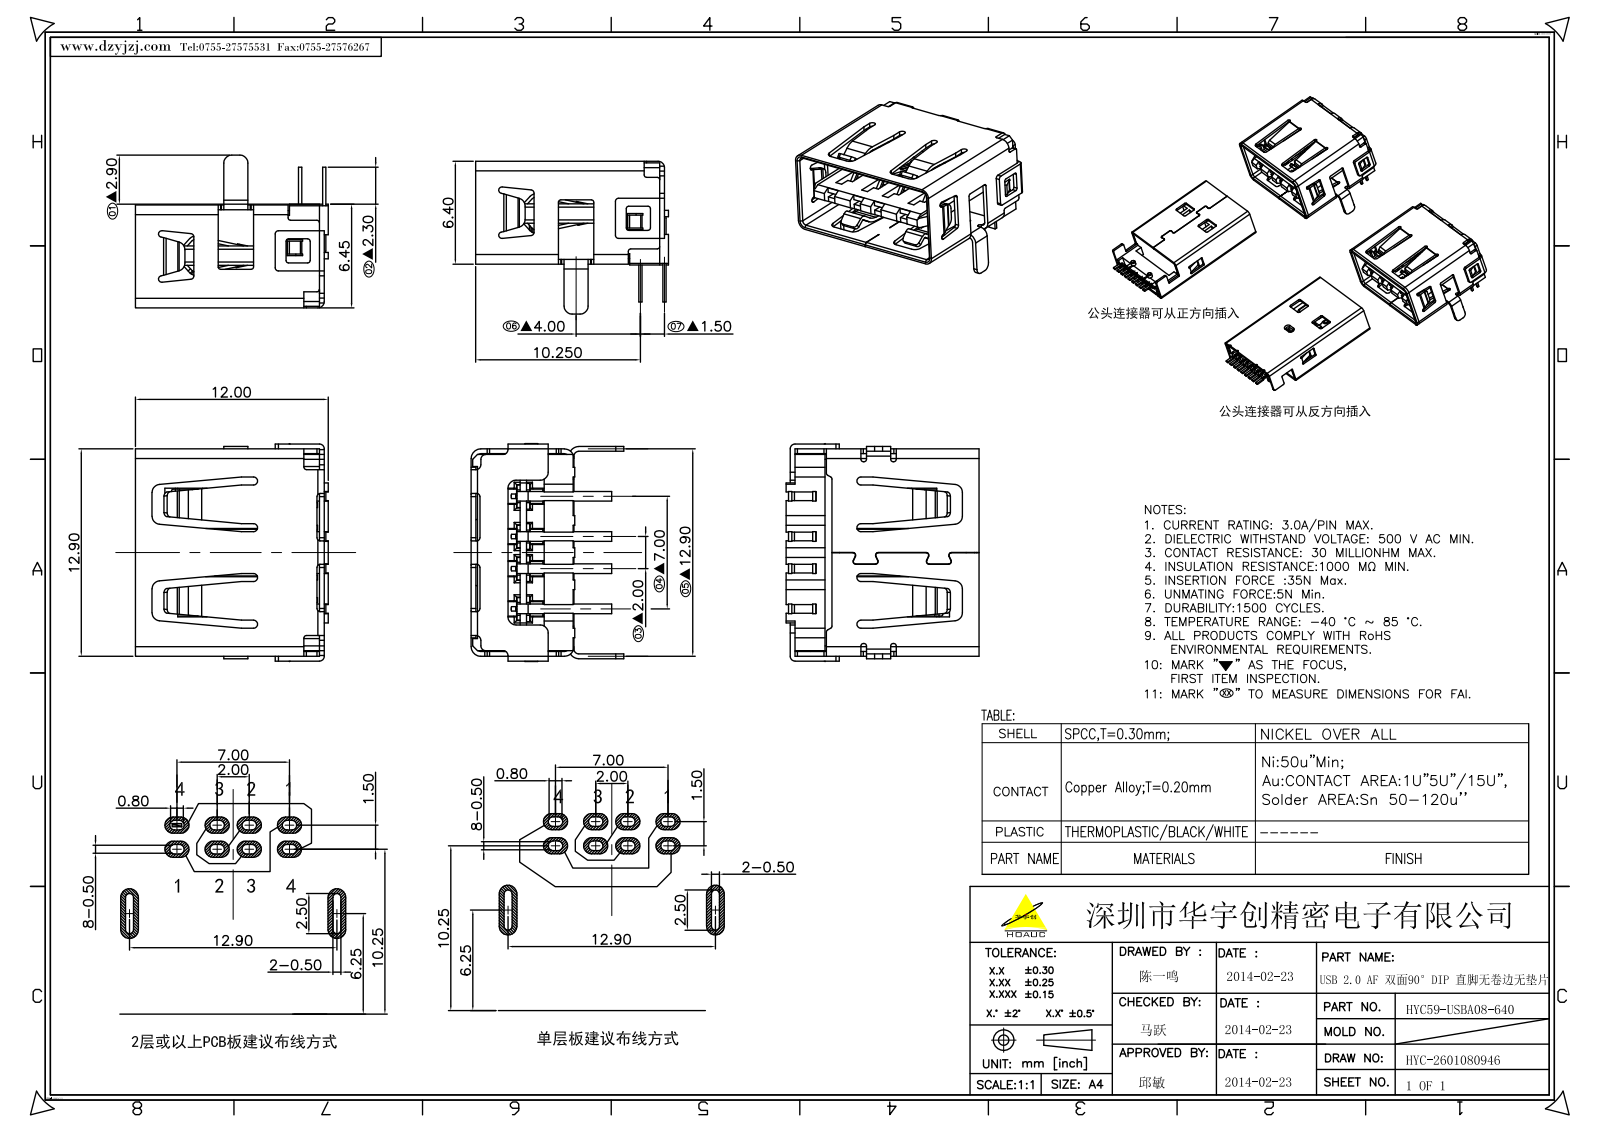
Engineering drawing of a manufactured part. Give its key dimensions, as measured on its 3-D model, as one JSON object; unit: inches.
{"part_name": "PRODUCT_2258", "step_written_by": "CREO PARAMETRIC BY PTC INC, 2022073 (AUTOMOTIVE_DESIGN)", "units": "inches", "bodies": {"solids": 1, "faces": 746, "planar": 507, "cylindrical": 215, "other": 24}, "overall_size": [0.533, 0.472, 0.374], "volume_in3": 0.027, "surface_area_in2": 2.128, "partial_cylinders_radius": [[0.006, 32], [0.008, 24], [0.012, 20], [0.004, 19], [0.02, 17], [0.01, 12], [0.024, 10], [0.007, 8]], "face_to_face_distances": [0.24, 0.136, 0.089, 0.14, 0.1, 0.228, 0.252, 0.496, 0.104, 0.148]}
